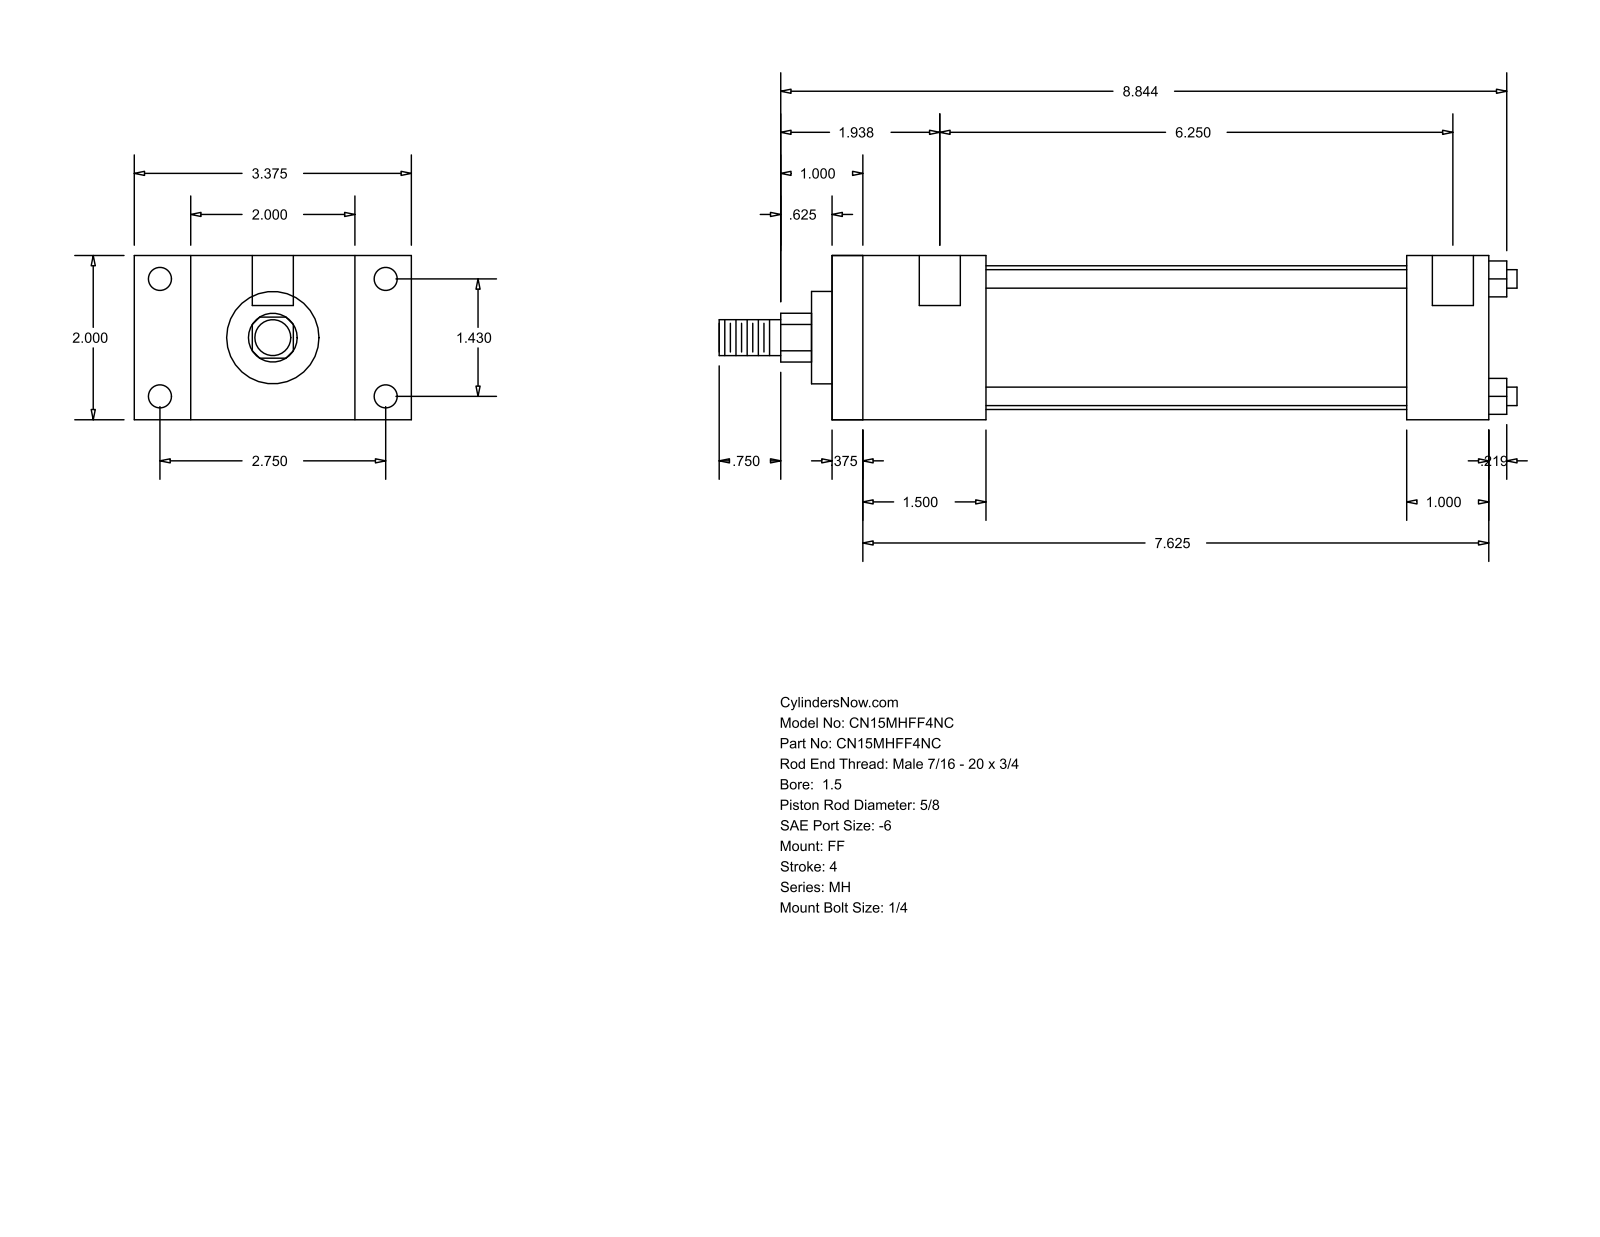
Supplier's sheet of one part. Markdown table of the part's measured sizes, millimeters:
| quantity | value |
| --- | --- |
| part name | MH_FF__0150_0.625 |
| STEP written by | GSSL Pune (CONFIG_CONTROL_DESIGN) |
| units | millimeters |
| bodies | 0 solids, 92 faces (64 planar, 28 cylindrical, 0 other) |
| overall size | 246.86 × 85.72 × 50.8 |
| round holes (diameter × count) | 5.56 × 4, 7.14 × 4, 12.7 × 2 |
| round bosses / shafts (diameter × count) | 5.71 × 4, 44.45 × 1, 28.57 × 1, 15.88 × 1, 11.11 × 1 |
| partial cylindrical surfaces (radius × count) | 7.54 × 1 |
| main face-to-face distances | 50.8, 203.19, 9.52, 193.67, 17.46, 68.26, 47.62, 38.1, 155.57, 177.8 |
| hole center spacings | 36.32, 69.84, 78.72, 161.92, 3.17, 158.75 |
